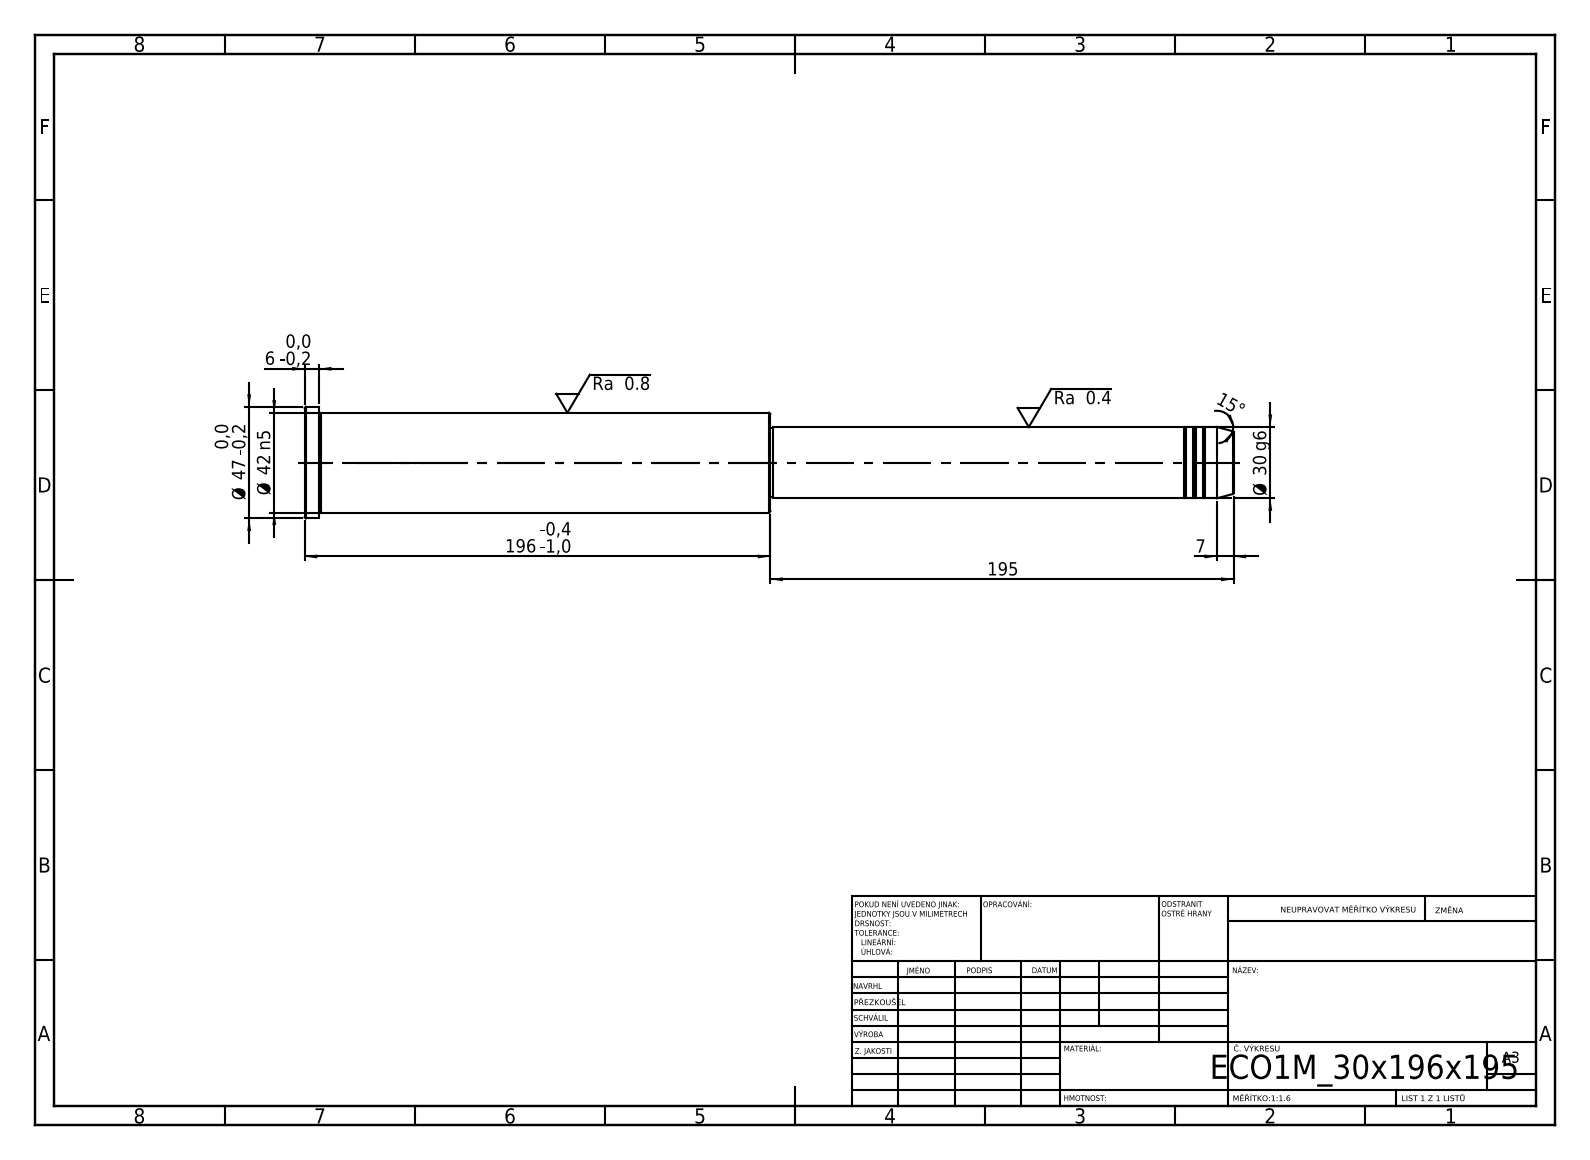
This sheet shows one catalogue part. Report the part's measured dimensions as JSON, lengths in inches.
{"step_written_by": "SolidWorks 2019 (CONFIG_CONTROL_DESIGN)", "units": "inches", "bodies": {"solids": 1, "faces": 43, "planar": 5, "cylindrical": 14, "other": 24}, "overall_size": [15.394, 1.85, 1.85], "volume_in3": 25.06, "surface_area_in2": 74.15, "round_bosses_or_shafts": [[1.85, 1], [1.654, 1], [1.181, 1], [1.142, 1]], "face_to_face_distances": [7.717, 7.677, 15.394, 15.157, 7.48, 0.236, 7.638, 0.039, 7.52, 7.756]}
